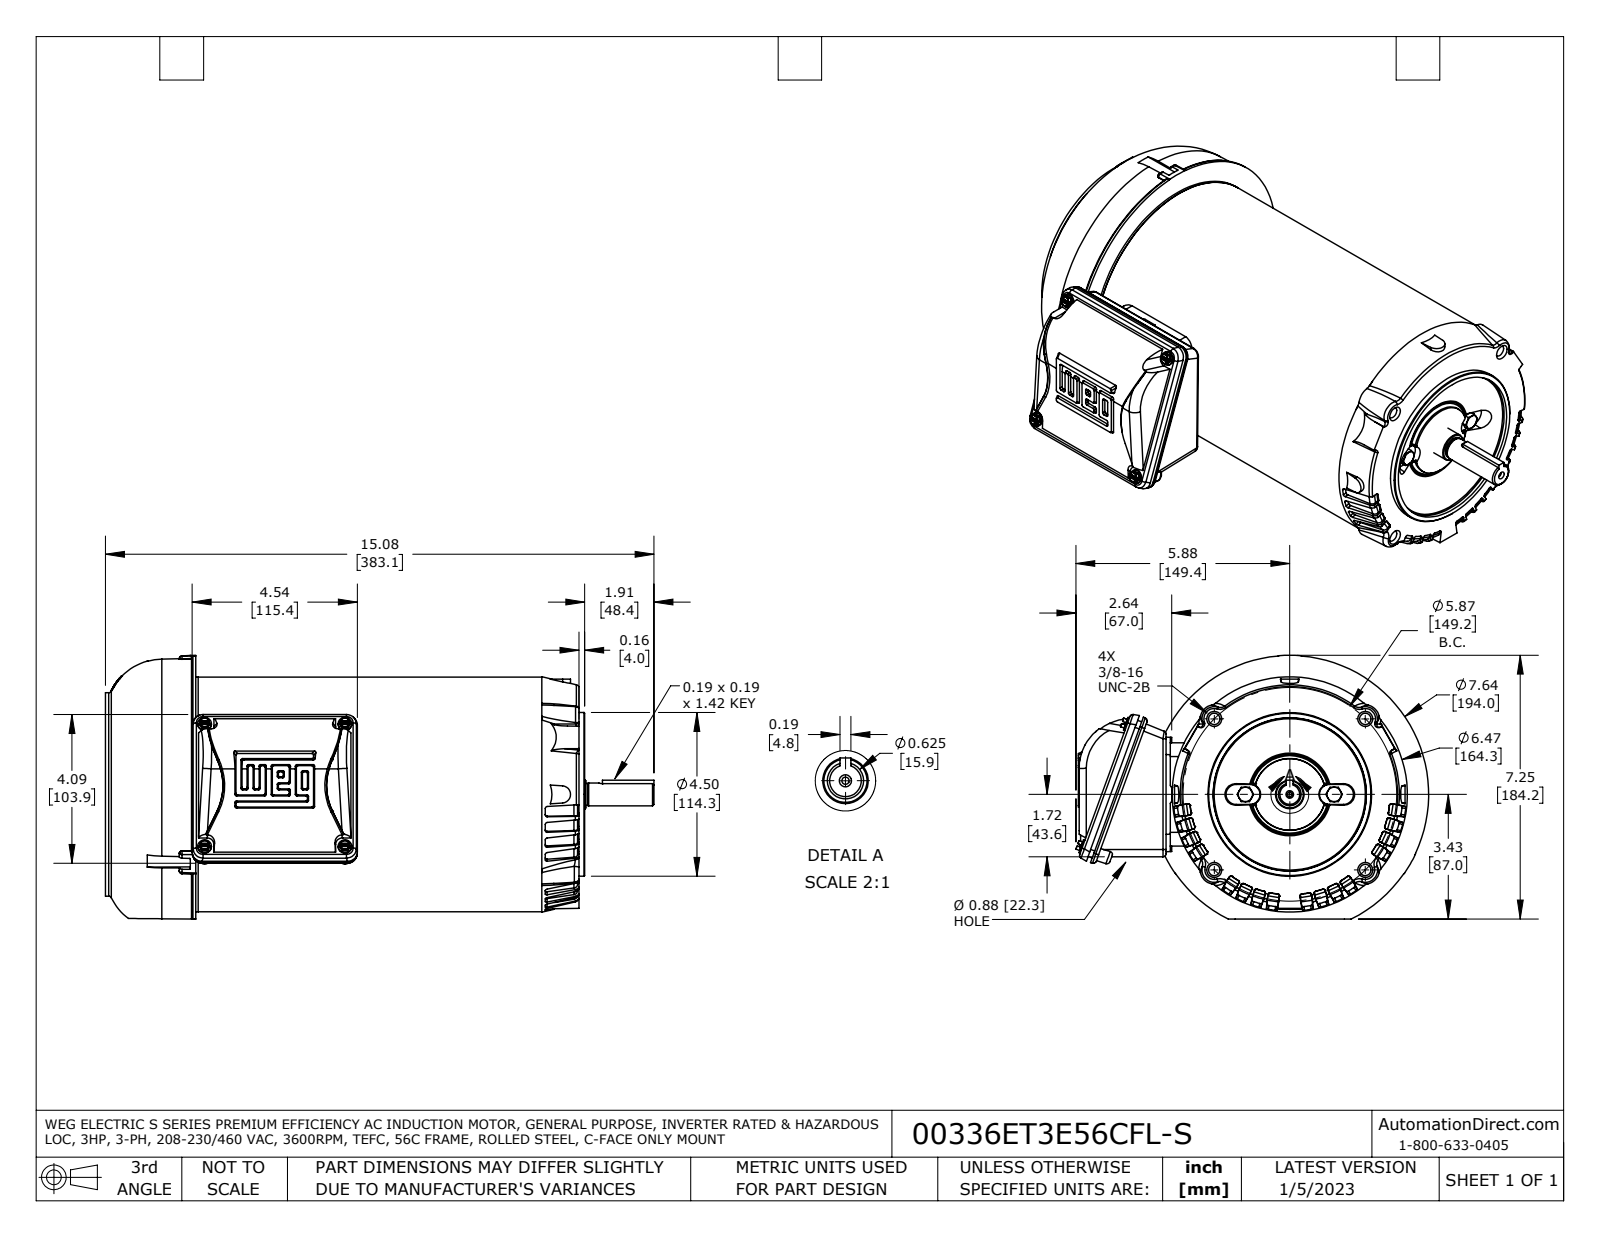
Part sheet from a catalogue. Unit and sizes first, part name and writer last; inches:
Units: inches
Overall size (bounding box): 15.083 × 9.7 × 7.551
Round holes (diameter × count): ⌀0.313 ×4, ⌀0.124 ×1
Round bosses / shafts (diameter × count): ⌀0.374 ×4, ⌀0.35 ×2, ⌀6.447 ×1, ⌀6.447 ×1, ⌀5.591 ×1, ⌀4.5 ×1, ⌀0.783 ×1, ⌀0.625 ×1
Partial cylindrical surfaces — rounded edges, fillets, slot ends (radius × count): R0.047 ×40, R0.006 ×38, R0.051 ×32, R0.059 ×12, R0.087 ×12, R0.02 ×10, R0.205 ×8, R0.276 ×8
Main face-to-face distances: 9.449, 0.067, 9.516, 2.283, 2.35, 11.799, 12.823, 10.539, 10.472, 1.024
Hole centre spacings: 2.937, 4.154, 5.874
Volume: 471.7 in³ · Surface area: 661.4 in²
Bodies: 13 solids, 1274 faces (471 planar, 275 cylindrical, 528 other)
Part name (STEP PRODUCT): 56C_3PH_TEFC_GP_15079_FL fxt
STEP written by: SolidWorks 2021 (AUTOMOTIVE_DESIGN)
